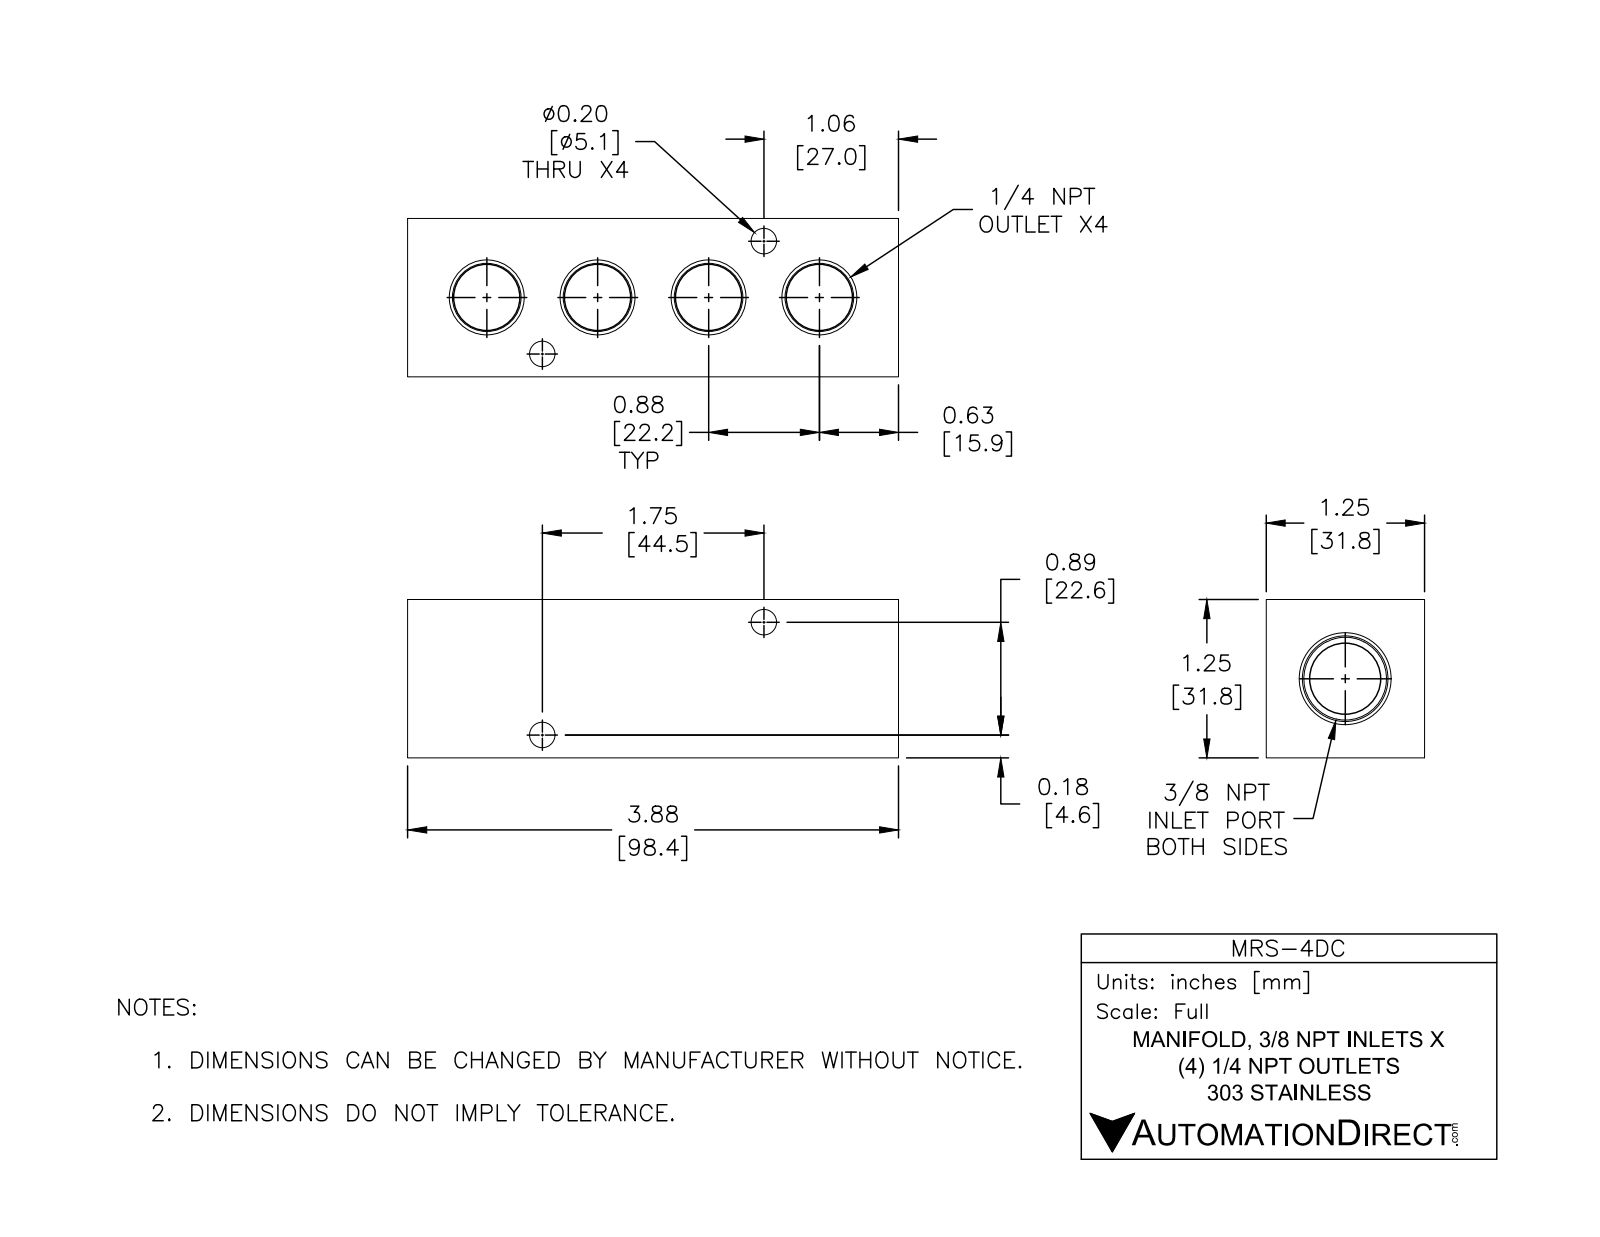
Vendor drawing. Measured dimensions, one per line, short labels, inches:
name: MRS-4DC
written by: SolidWorks 2015 (CONFIG_CONTROL_DESIGN)
unit: in
bodies: 1 solid, 66 faces (16 planar, 26 cylindrical, 24 other)
size: 3.875 × 1.25 × 1.25
volume: 4.537 in³; area: 32.47 in²
holes: 4× ⌀0.2, 1× ⌀0.562
rounds: 4× R0.219
face distances: 1.25, 3.875, 0.41, 3.465, 0.86, 0.39, 3.055
hole spacings: 1.963
